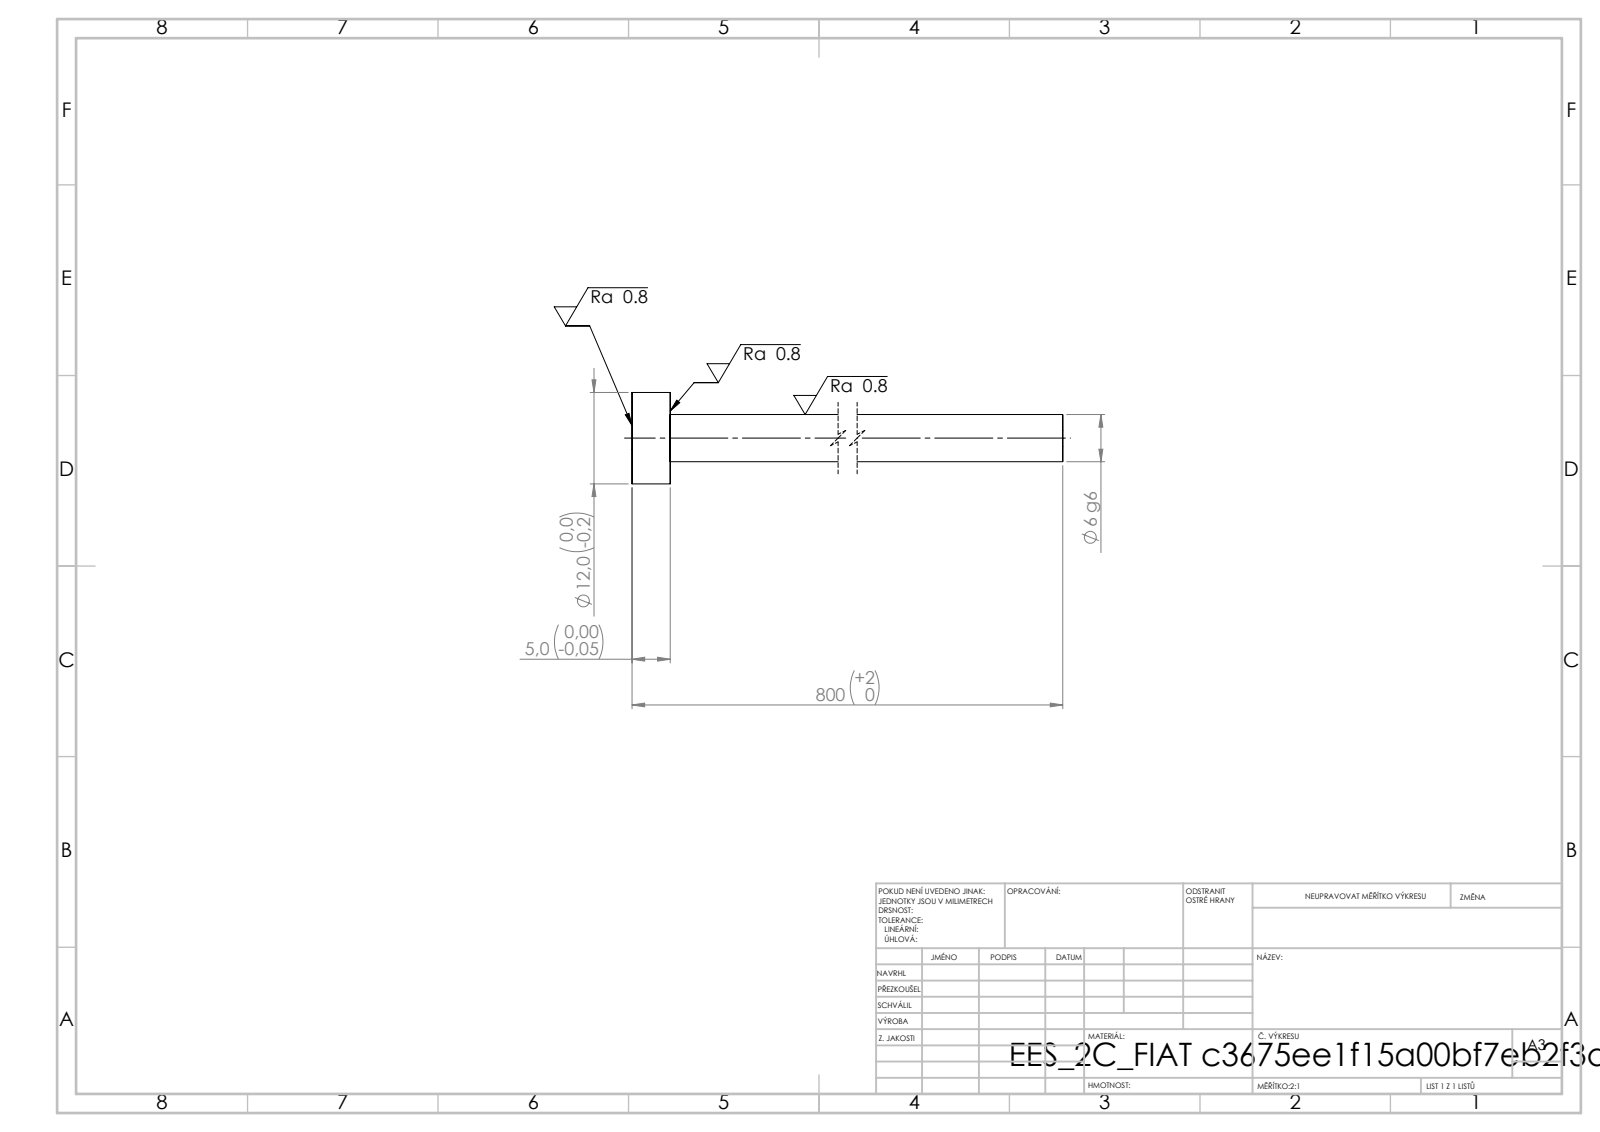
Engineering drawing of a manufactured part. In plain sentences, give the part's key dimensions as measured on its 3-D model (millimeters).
Its 3-D file was written by "SolidWorks 2019 (CONFIG_CONTROL_DESIGN)". It is 1 solid with 7 faces: 3 planar, 4 cylindrical and 0 other. Overall it measures 800 by 12 by 12 millimeters. Its volume is 24 567 cubic millimeters and its surface area 15 900 square millimeters. Round bosses or shafts: 1 of diameter 12, 1 of diameter 6.2. The main face-to-face distances are 5, 800, 795.
